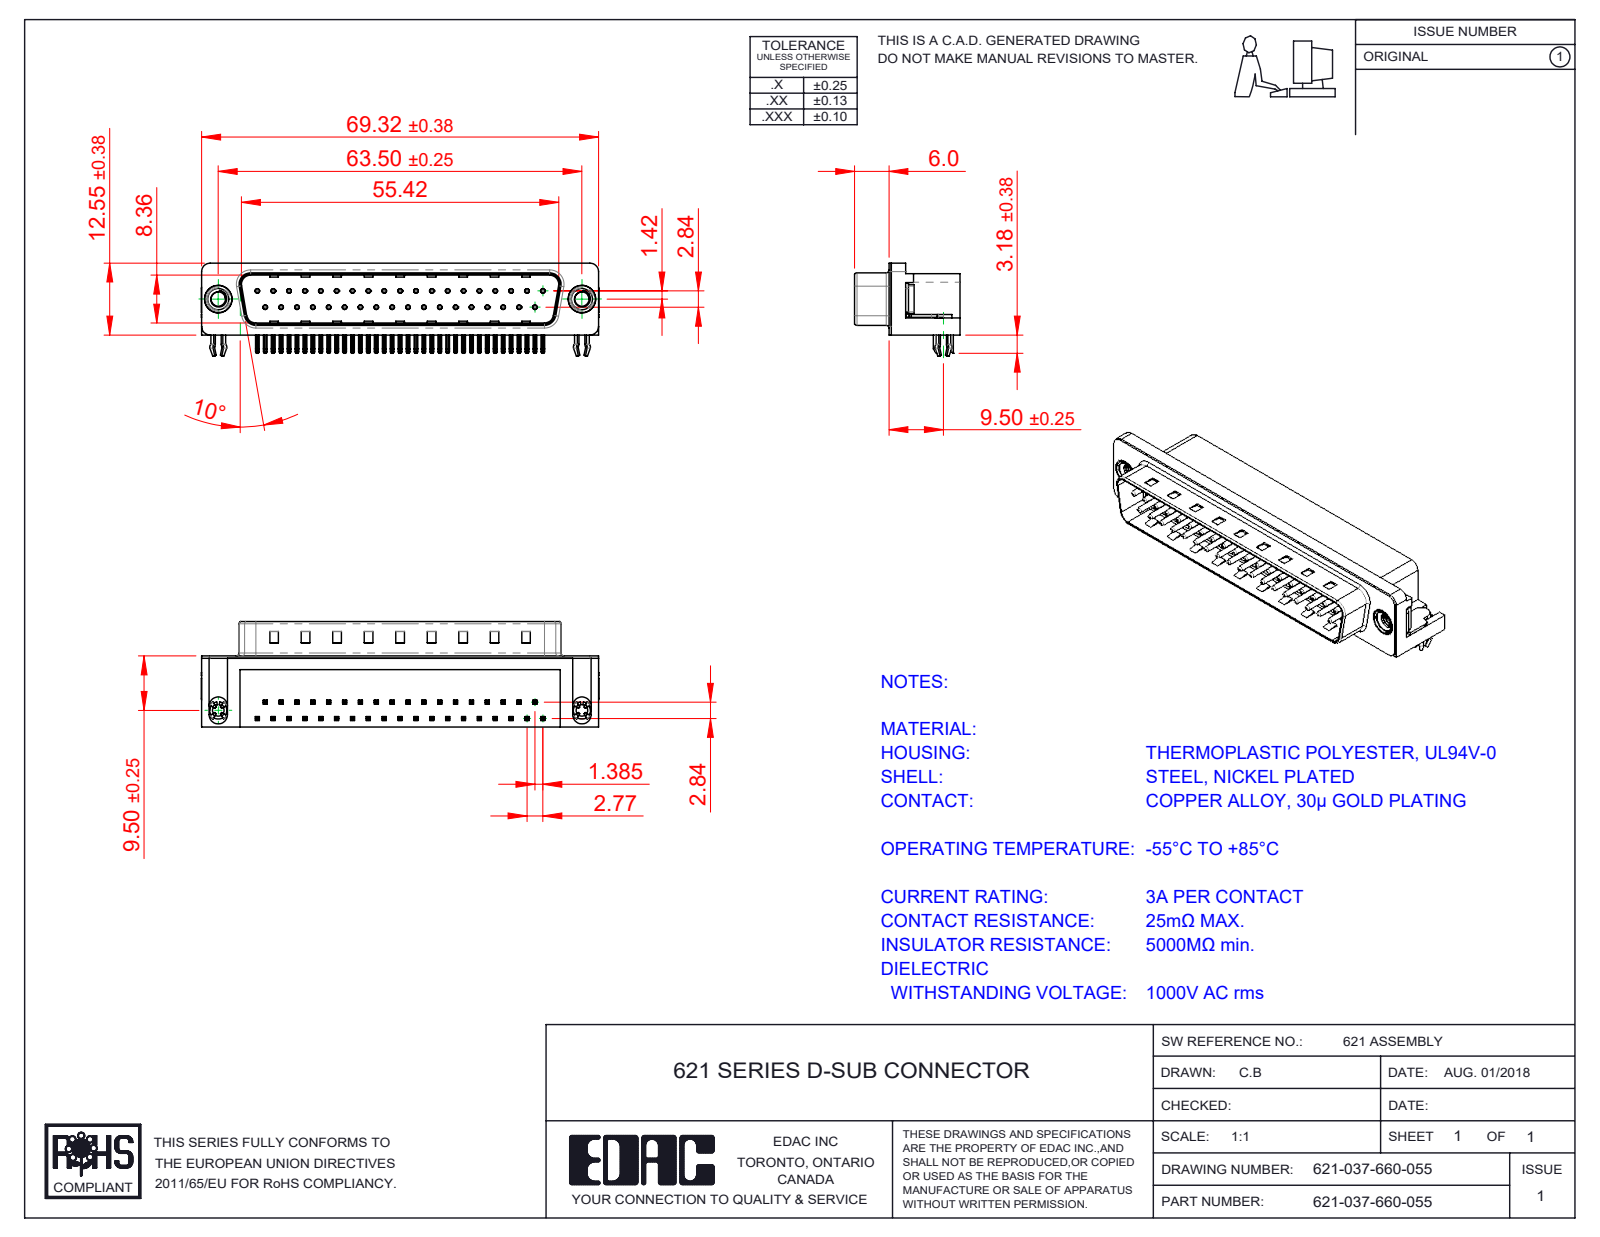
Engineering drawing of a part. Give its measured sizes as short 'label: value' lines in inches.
name: 621 M3 Threaded Rivet; 621 Shell_37 Socket; 621 Contact Top; 621 Contact Bottom (+3 more)
written by: SolidWorks 2016 (CONFIG_CONTROL_DESIGN)
unit: in
bodies: 43 solids, 3229 faces (2013 planar, 931 cylindrical, 285 other)
size: 2.732 × 0.724 × 0.619
volume: 0.526 in³; area: 15.77 in²
holes: 37× ⌀0.014, 37× ⌀0.031, 2× ⌀0.089, 2× ⌀0.098, 2× ⌀0.157, 2× ⌀0.189, 2× ⌀0.197
bosses: 37× ⌀0.03, 2× ⌀0.193, 2× ⌀0.187, 2× ⌀0.154, 2× ⌀0.128
rounds: 156× R0.01, 74× R0.005, 16× R0.039, 9× R0.02, 8× R0.063, 7× R0.059, 4× R0.035, 4× R0.079
face distances: 0.016, 0.472, 0.407, 0.345, 0.083, 0.067, 0.412, 0.428, 0.354, 0.488
hole spacings: 0.124, 0.109, 0.218, 0.327, 0.436, 0.545, 0.763, 0.872
